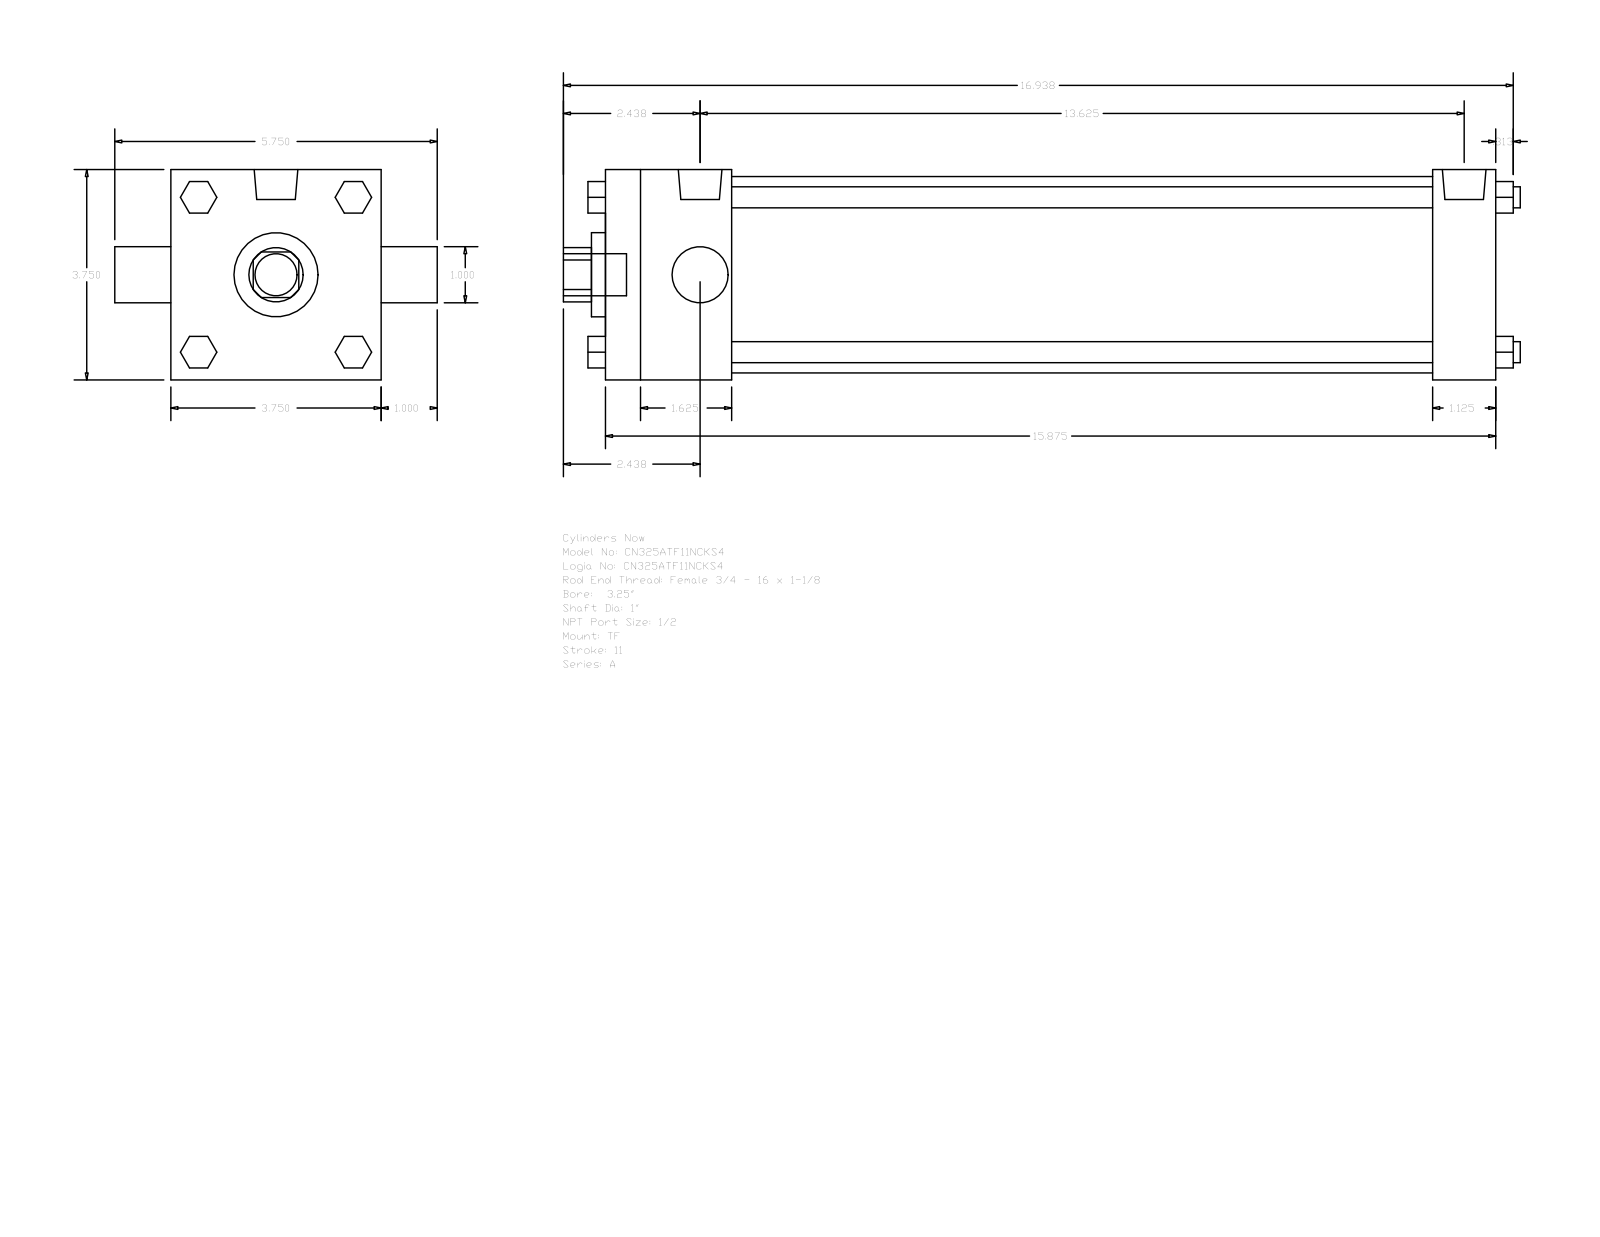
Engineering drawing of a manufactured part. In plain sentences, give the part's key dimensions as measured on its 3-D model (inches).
The part is named "A_TF__0325_1". Its 3-D file was written by "GSSL Pune (CONFIG_CONTROL_DESIGN)". It is 0 solids with 120 faces: 92 planar, 28 cylindrical and 0 other. Overall it measures 17.063 by 5.75 by 3.75 inches. Round holes: 2 of diameter 1, 1 of diameter 1.5, 1 of diameter 3.5. Round bosses or shafts: 4 of diameter 0.375, 3 of diameter 0.344, 2 of diameter 0.778, 1 of diameter 0.75. Partial cylindrical surfaces (rounded edges, fillets, slot ends): 1 of radius 0.484. The main face-to-face distances are 3.75, 15.875, 1.125, 2.25, 14.75, 12.5, 13.625, 0.562, 1.38, 2.39.
